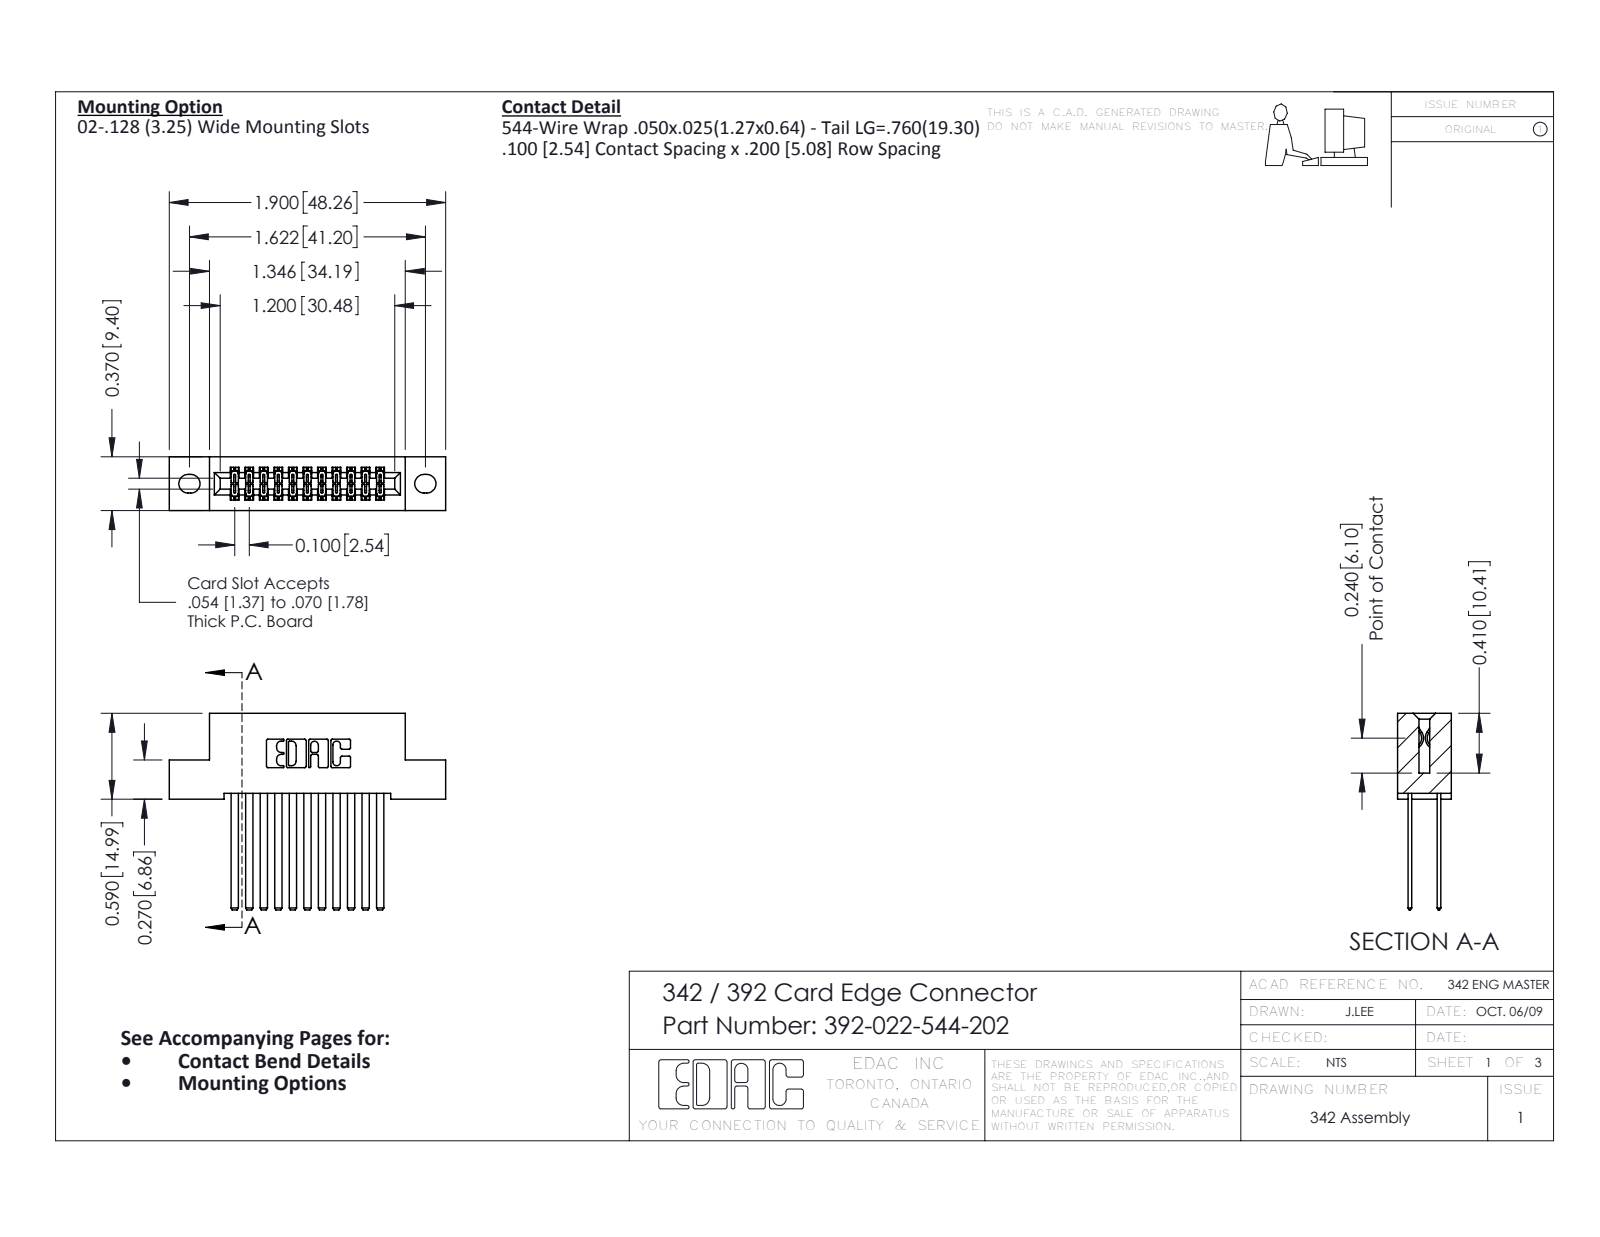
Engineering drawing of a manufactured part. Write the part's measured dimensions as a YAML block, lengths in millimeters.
part_name: "345-292-001_345-293-144; 392-022-544-202; 342 Part_.128 Slot"
step_written_by: "SolidWorks 2016 (CONFIG_CONTROL_DESIGN)"
units: millimeters
bodies: {solids: 23, faces: 1126, planar: 774, cylindrical: 352, other: 0}
overall_size: [48.3, 34.3, 9.4]
volume: 4440
surface_area: 7084
partial_cylinders:
  - {radius: 0.2, count: 33}
  - {radius: 0.3, count: 22}
  - {radius: 0.2, count: 6}
  - {radius: 0.8, count: 6}
  - {radius: 1.6, count: 4}
  - {radius: 0.7, count: 3}
  - {radius: 0.4, count: 2}
  - {radius: 0.6, count: 2}
face_to_face_distances: [5.1, 1.8, 7.6, 2.5, 6.9, 0.6, 5.7, 2.5, 9.4, 1]
